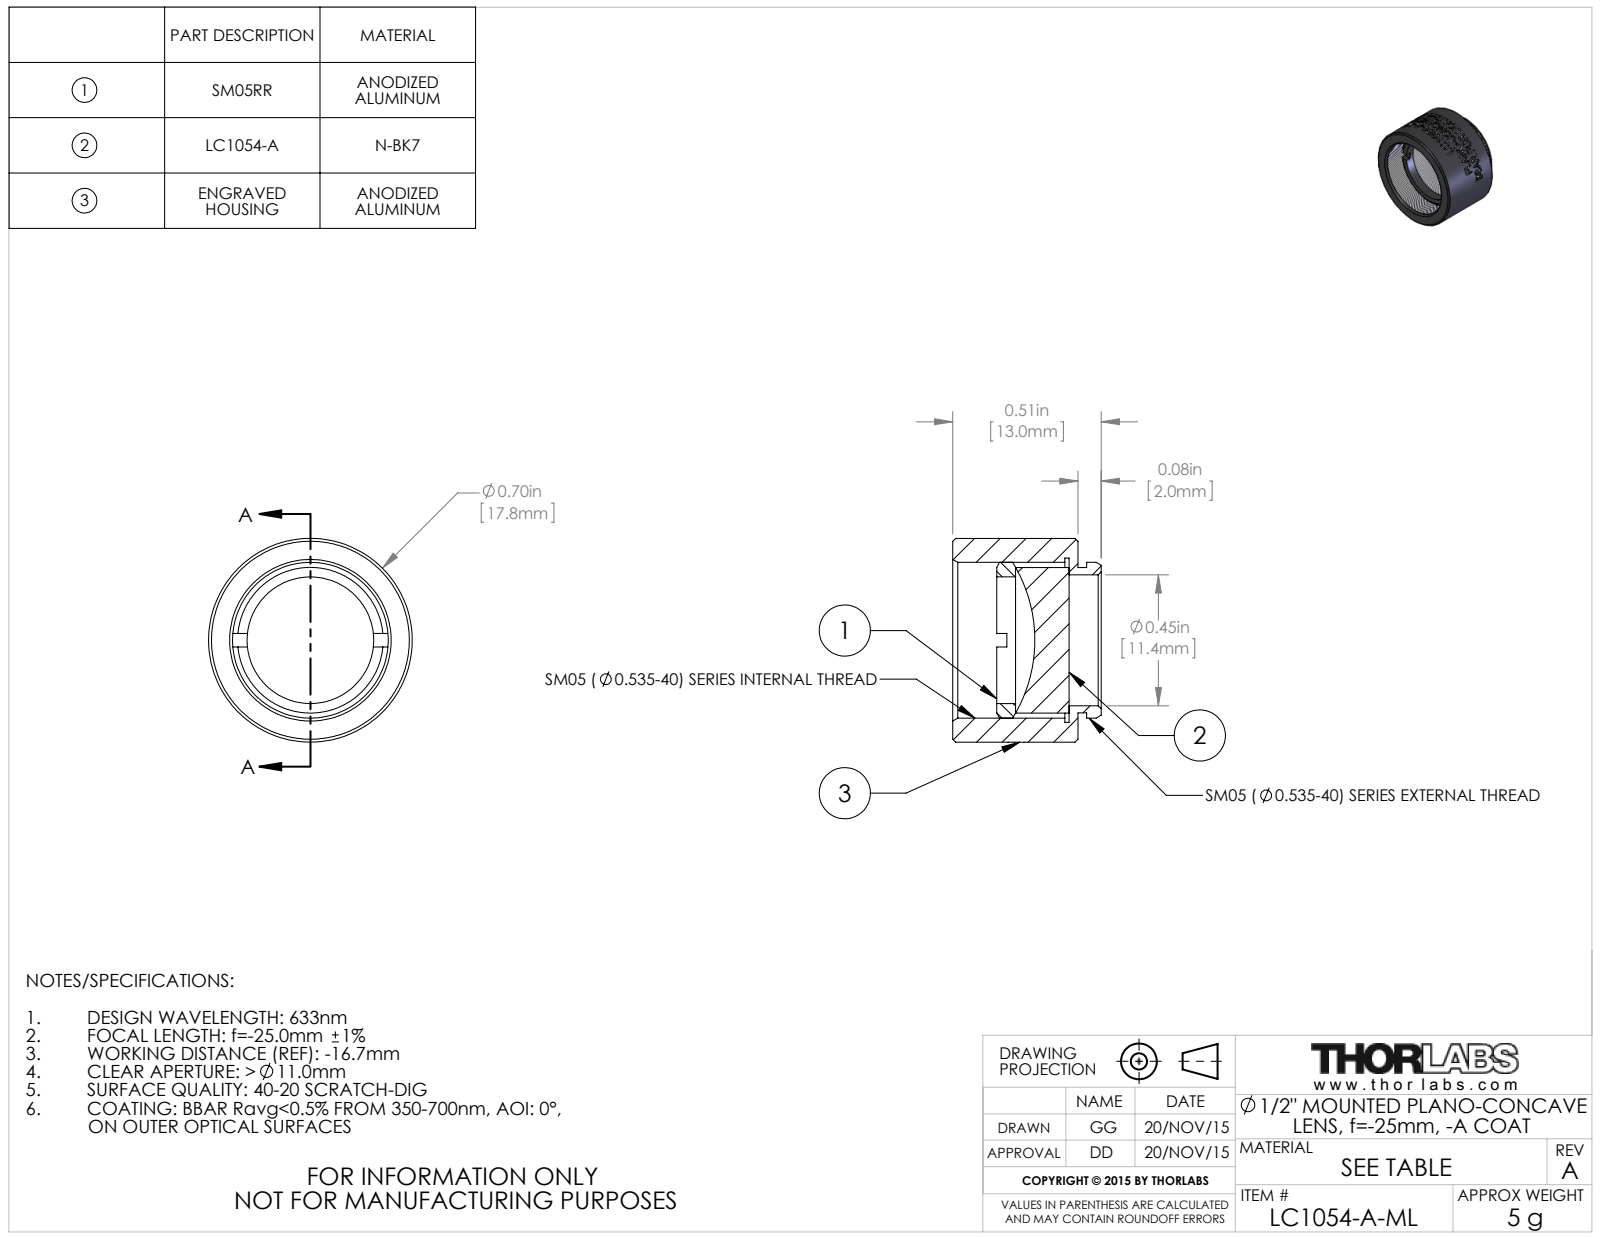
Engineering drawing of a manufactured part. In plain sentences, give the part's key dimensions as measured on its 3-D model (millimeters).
The part is named "TTN045236-E0W". Its 3-D file was written by "SolidWorks 2014 (CONFIG_CONTROL_DESIGN)". It is 3 solids with 144 faces: 16 planar, 111 cylindrical and 17 other. Overall it measures 17.8 by 17.8 by 13 millimeters. Its volume is 1 770 cubic millimeters and its surface area 2 214 square millimeters. Round holes: 1 of diameter 11, 1 of diameter 11.4, 1 of diameter 13.6, 1 of diameter 14.4. Round bosses or shafts: 1 of diameter 17.8, 1 of diameter 13.6, 1 of diameter 12.7, 1 of diameter 12.7. The main face-to-face distances are 0.8, 10.9, 10.2, 5.4, 4.7, 5.5, 7.1, 6.3, 1.7, 3.8.
